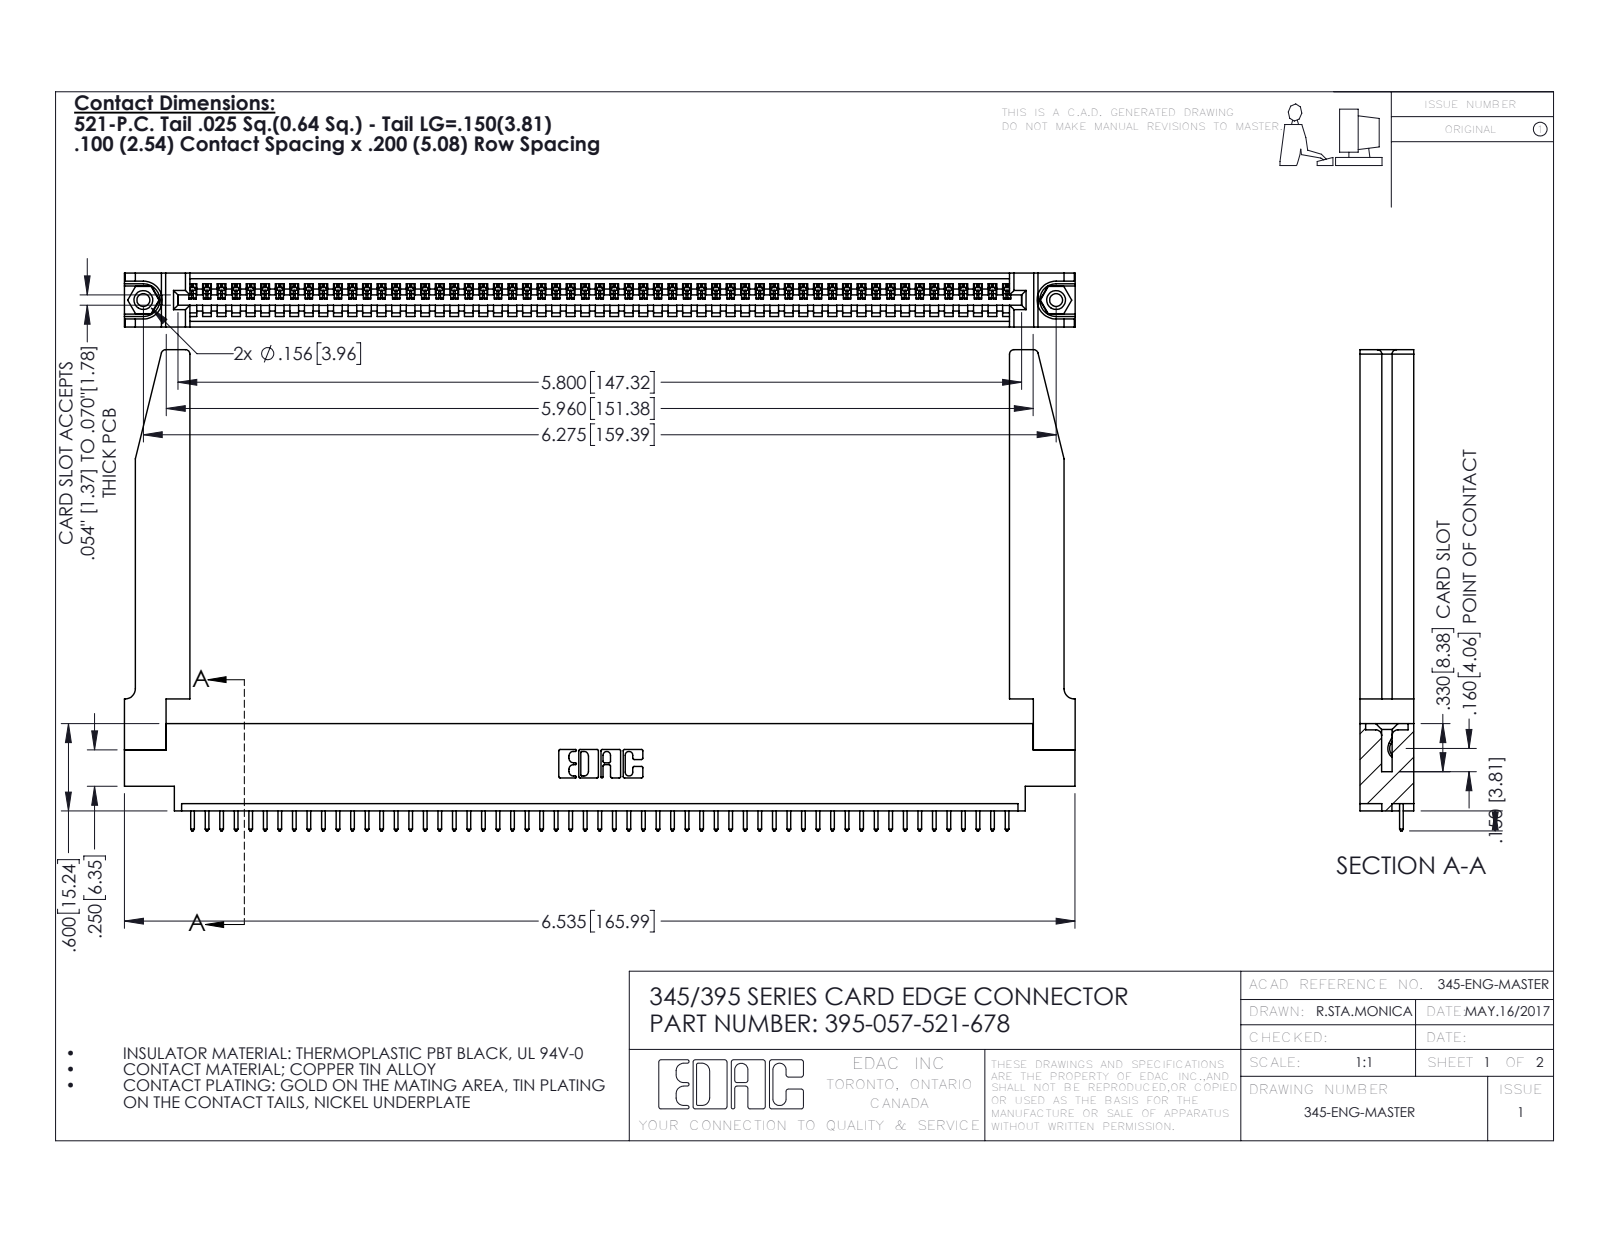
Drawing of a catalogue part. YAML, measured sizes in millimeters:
part_name: "345-250-001_345-250-001-102; 345-220-078_345-220-078; 395-057-521-678; 345-292-001_345-293-121 (+1 more)"
step_written_by: "SolidWorks 2016 (CONFIG_CONTROL_DESIGN)"
units: millimeters
bodies: {solids: 62, faces: 3670, planar: 2506, cylindrical: 1112, other: 52}
overall_size: [166, 84, 9.4]
volume: 23380
surface_area: 27290
round_holes:
  - {diameter: 2.3, count: 2}
  - {diameter: 3.2, count: 2}
  - {diameter: 4, count: 2}
  - {diameter: 1.6, count: 1}
round_bosses_or_shafts:
  - {diameter: 3.9, count: 2}
partial_cylinders:
  - {radius: 0.2, count: 114}
  - {radius: 0.3, count: 114}
  - {radius: 0.3, count: 22}
  - {radius: 0.8, count: 8}
  - {radius: 0.2, count: 6}
  - {radius: 0.8, count: 6}
  - {radius: 0.7, count: 3}
  - {radius: 0.8, count: 2}
face_to_face_distances: [9.4, 1.8, 7.6, 2.5, 6.9, 0.6, 5.1, 5.7, 3.8, 3.8]
hole_center_spacings: [6.9, 153.4, 159.4]
